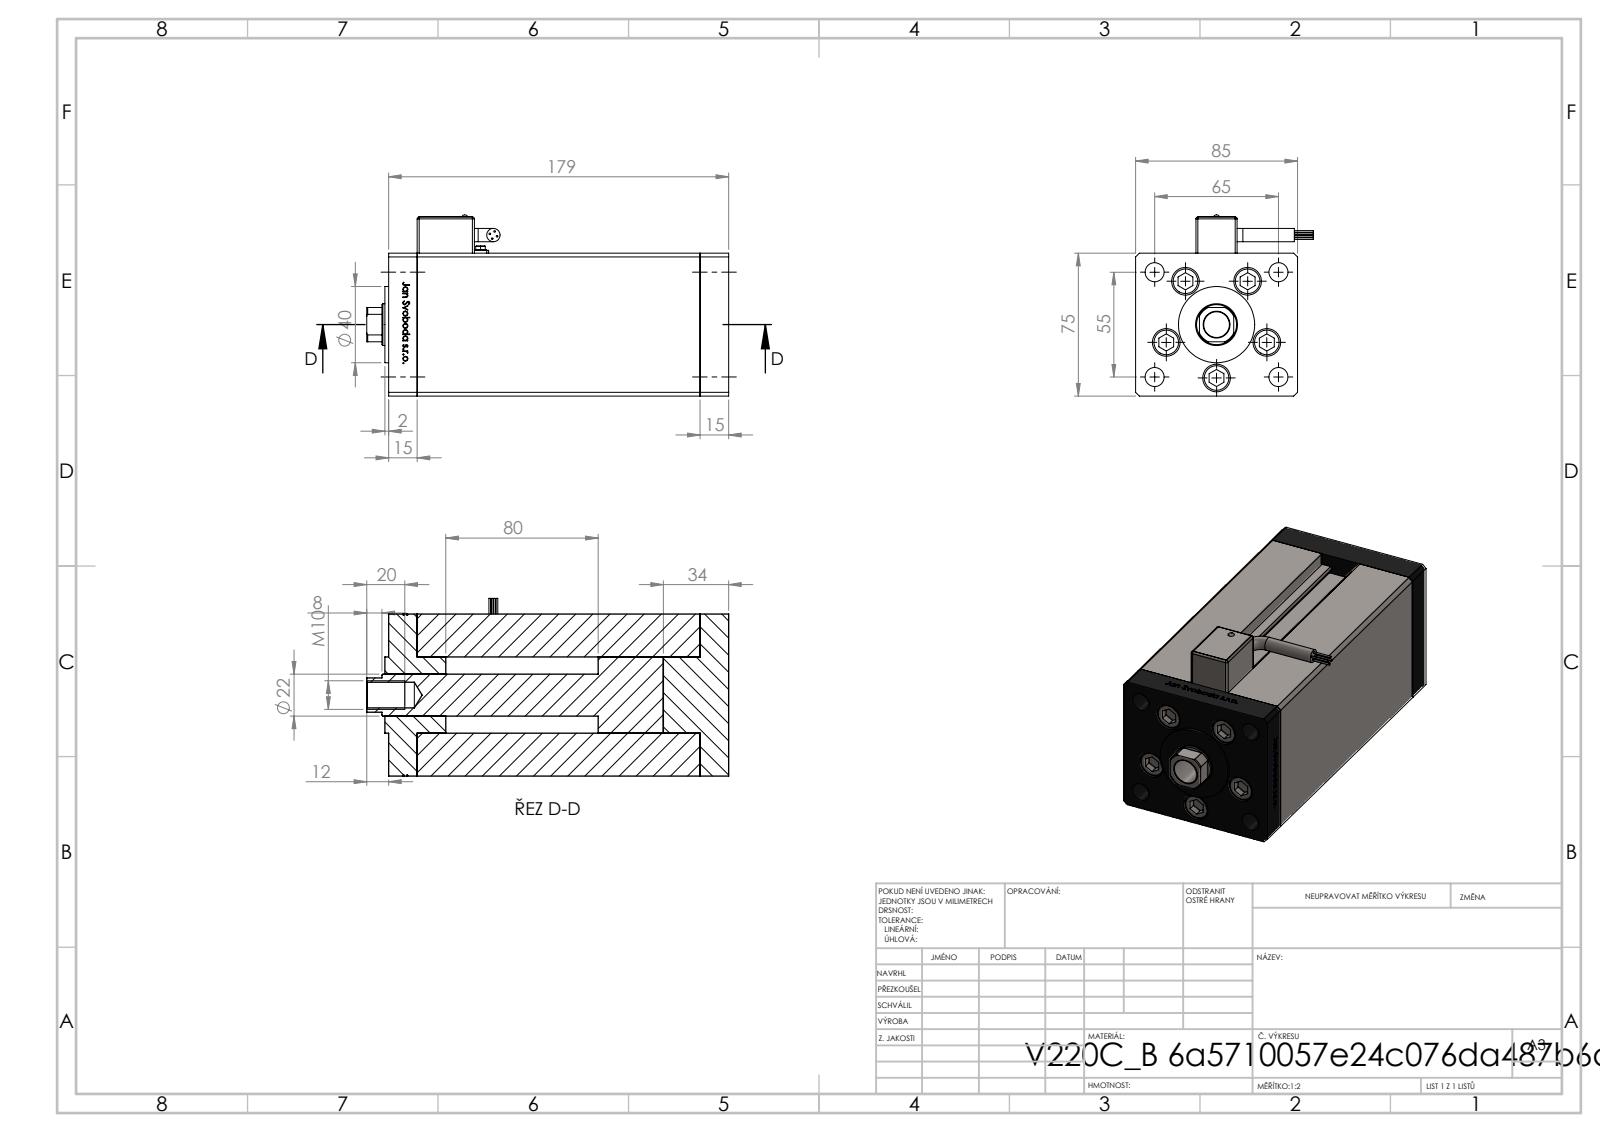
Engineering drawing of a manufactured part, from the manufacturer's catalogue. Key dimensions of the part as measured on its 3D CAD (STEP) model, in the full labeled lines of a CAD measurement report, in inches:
Part name (STEP PRODUCT): ALLEN BOLT; V220C BACK_B; V220C_FRONT_B; V220C_B MIDDLE (+2 more)
STEP written by: SolidWorks 2019 (CONFIG_CONTROL_DESIGN)
Units: inches
Bodies: 15 solids, 1287 faces (503 planar, 192 cylindrical, 592 other)
Overall size (bounding box): 7.48 × 3.744 × 3.673
Volume: 62.85 in³ · Surface area: 257.5 in²
Round holes (diameter × count): ⌀0.433 ×5, ⌀0.571 ×5, ⌀0.394 ×4, ⌀0.079 ×2, ⌀0.518 ×2, ⌀0.142 ×1, ⌀0.197 ×1, ⌀0.276 ×1, ⌀0.531 ×1, ⌀0.866 ×1
Round bosses / shafts (diameter × count): ⌀0.315 ×5, ⌀0.033 ×4, ⌀0.276 ×2, ⌀1.575 ×1, ⌀0.236 ×1, ⌀0.138 ×1, ⌀0.098 ×1
Partial cylindrical surfaces — rounded edges, fillets, slot ends (radius × count): R0.039 ×14, R0.037 ×2, R0.157 ×2, R0.413 ×1
Main face-to-face distances: 3.346, 2.953, 0.591, 5.846, 6.437, 7.028, 1.348, 2.697, 0.758, 5.089
Hole centre spacings: 1.102, 1.676, 0.664, 0.755, 1.273, 1.28, 1.324, 1.47
